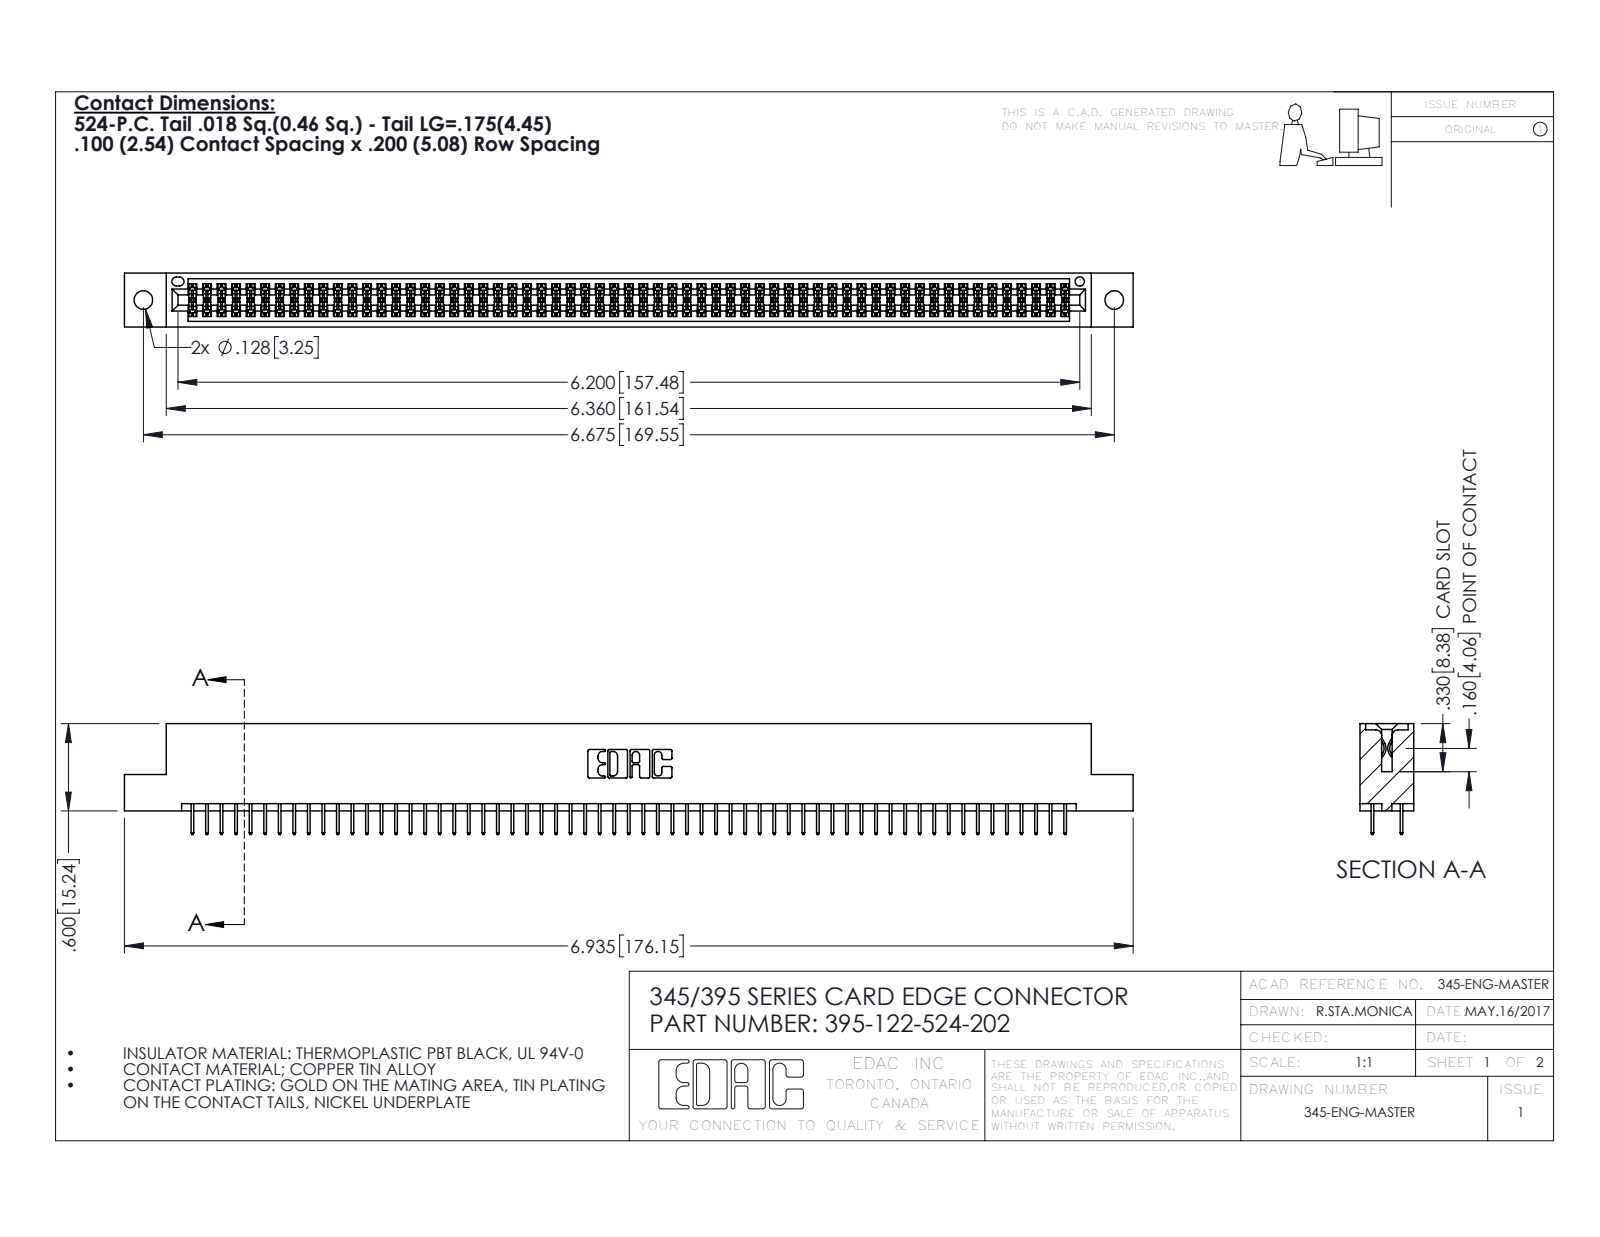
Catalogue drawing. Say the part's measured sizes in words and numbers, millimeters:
The part is named "345 Part_Flush Mounting Lugs - 0.128 Dia; 345-292-001_345-293-124; 395-122-524-202". Its 3-D file was written by "SolidWorks 2016 (CONFIG_CONTROL_DESIGN)". It is 123 solids with 6714 faces: 4838 planar, 1876 cylindrical and 0 other. Overall it measures 176.1 by 19.4 by 9.4 millimeters. Its volume is 17 060 cubic millimeters and its surface area 24 830 square millimeters. Round holes: 2 of diameter 3.3, 1 of diameter 1.6. Partial cylindrical surfaces (rounded edges, fillets, slot ends): 183 of radius 0.2, 22 of radius 0.3, 6 of radius 0.2, 6 of radius 0.8, 3 of radius 0.7, 2 of radius 0.4, 2 of radius 0.5, 2 of radius 0.6. The main face-to-face distances are 7.6, 1.8, 5.1, 9.4, 2.5, 6.9, 0.6, 5.7, 1.8, 4.4. The hole center spacings are 6.9, 163.6, 169.5.
